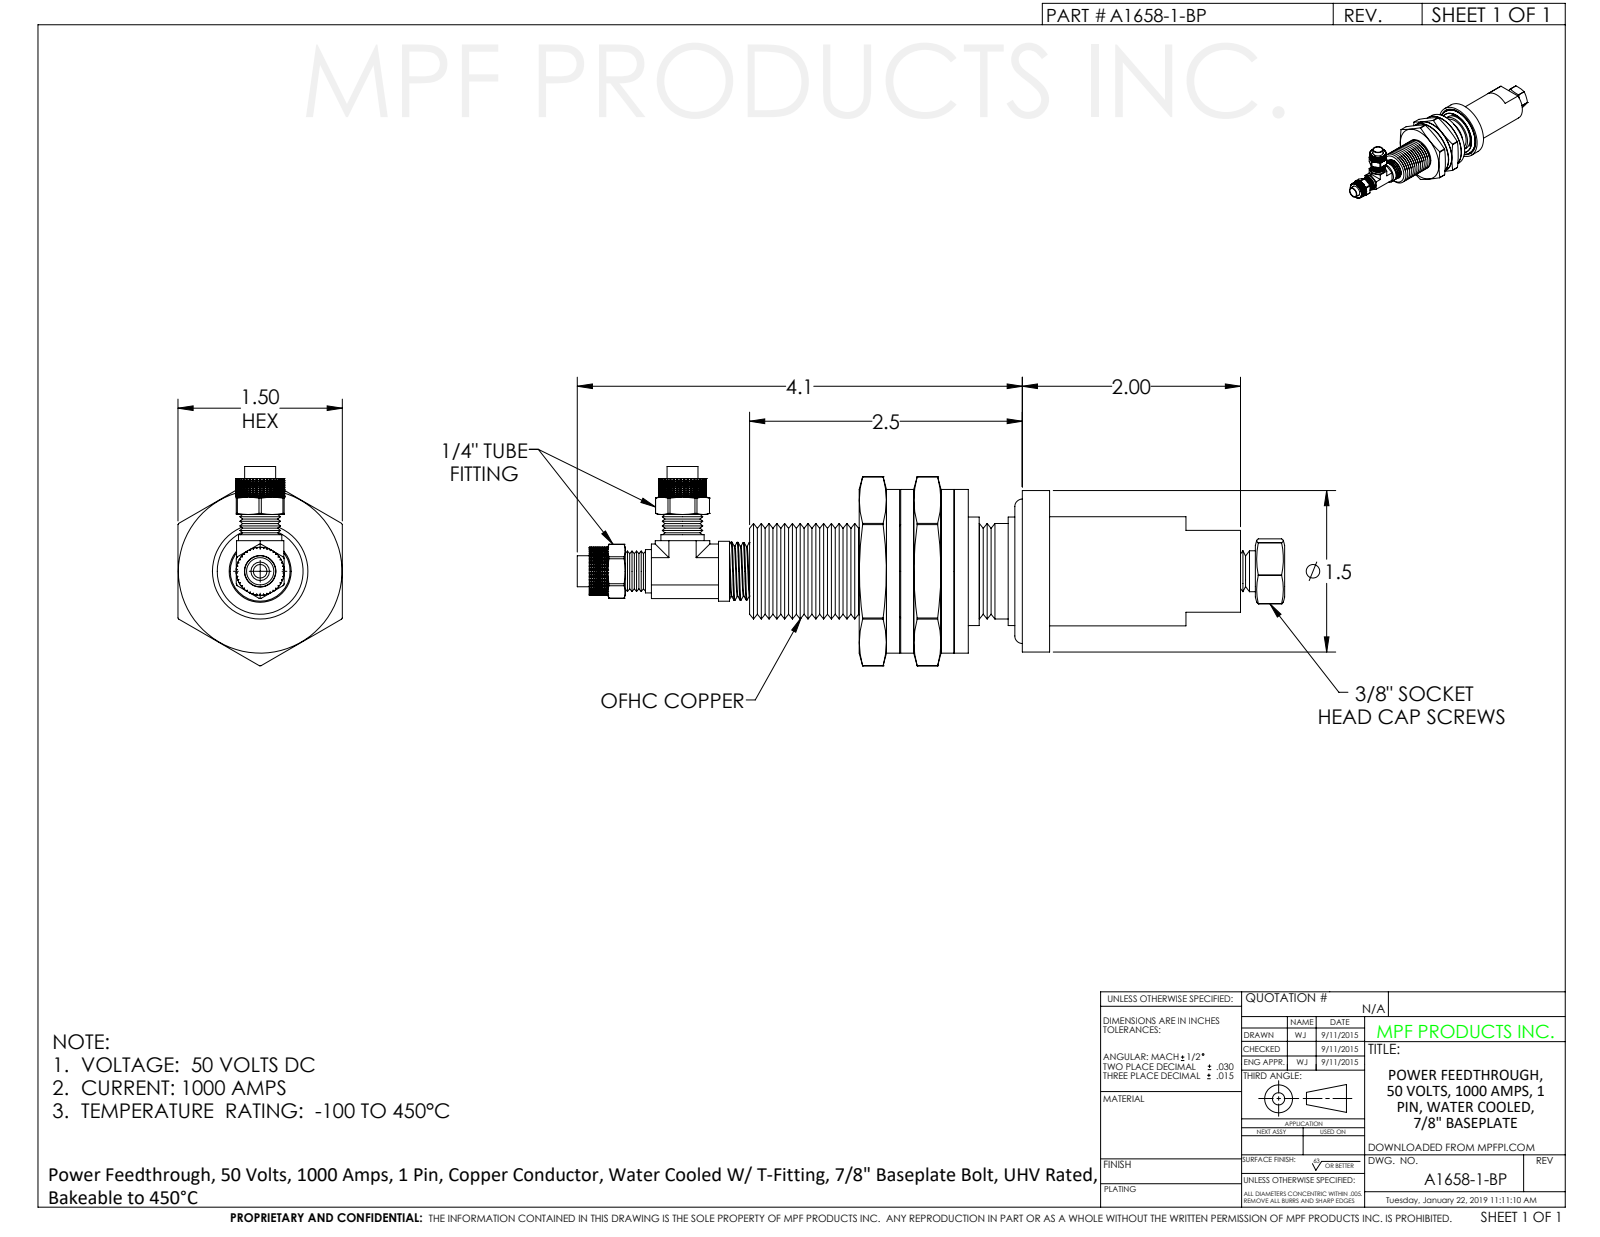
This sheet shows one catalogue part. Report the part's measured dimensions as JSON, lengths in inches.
{"part_name": "A1658-1-BP; A1659-5; A0377-7; A1662-1 (+6 more)", "step_written_by": "SolidWorks 2012 (CONFIG_CONTROL_DESIGN)", "units": "inches", "bodies": {"solids": 12, "faces": 625, "planar": 93, "cylindrical": 119, "other": 413}, "overall_size": [6.374, 1.836, 1.506], "volume_in3": 4.546, "surface_area_in2": 65.01, "round_holes": [[0.082, 1], [0.09, 1], [0.125, 1], [0.125, 1], [0.126, 1], [0.157, 1], [0.176, 1], [0.185, 1], [0.221, 1], [0.25, 1], [0.253, 1], [0.298, 1]], "round_bosses_or_shafts": [[0.437, 2], [1.5, 1], [1.48, 1], [1.303, 1], [1.125, 1], [1, 1], [0.995, 1], [0.875, 1]], "partial_cylinders_radius": [[0.02, 8], [0.25, 2], [0.201, 1], [0.324, 1], [0.866, 1]], "face_to_face_distances": [0.25, 0.5, 0.12, 0.37, 0.13, 0.38, 0.62, 0.75, 0.1, 0.87]}
